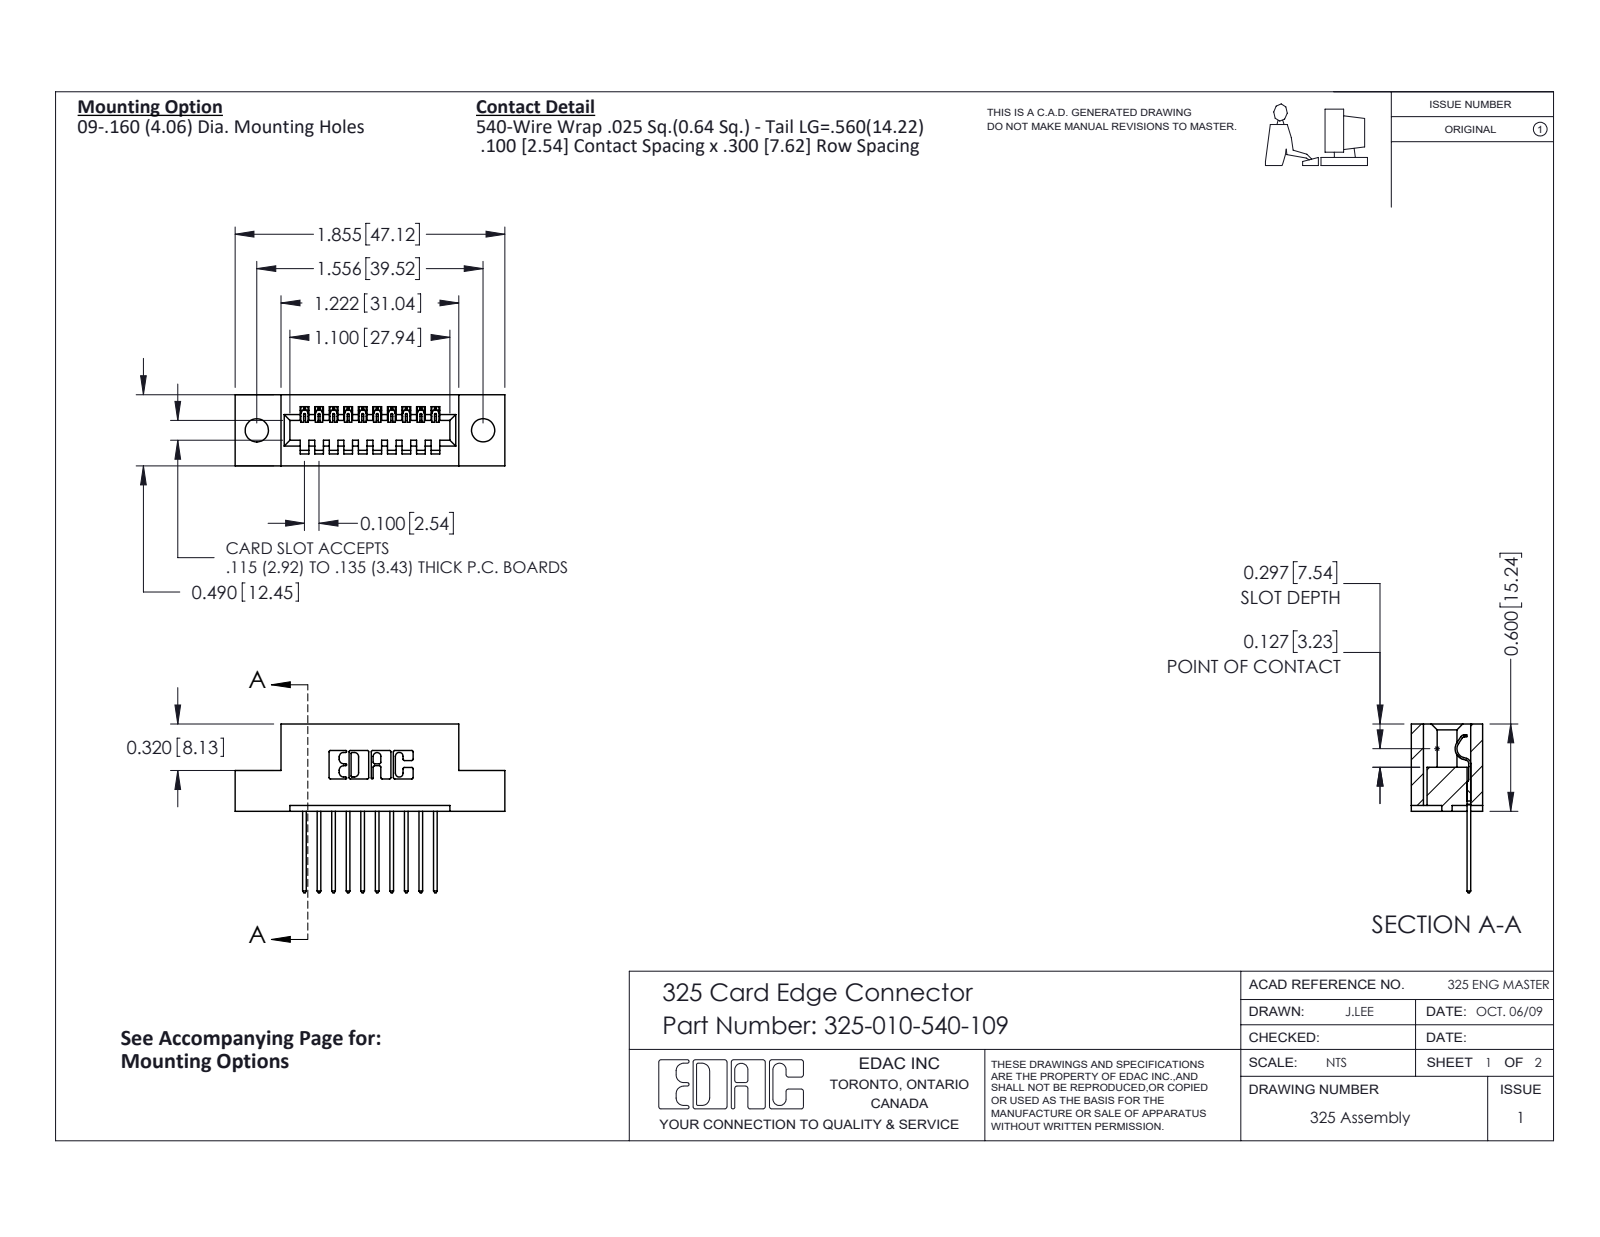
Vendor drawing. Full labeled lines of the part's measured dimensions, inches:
Part name (STEP PRODUCT): 325-010-540-109; 325-292-001_325-293-140; 325 Part_.160 TH
STEP written by: SolidWorks 2016 (CONFIG_CONTROL_DESIGN)
Units: inches
Bodies: 11 solids, 694 faces (490 planar, 204 cylindrical, 0 other)
Overall size (bounding box): 1.855 × 1.16 × 0.49
Volume: 0.336 in³ · Surface area: 8.487 in²
Round holes (diameter × count): ⌀0.16 ×2
Partial cylindrical surfaces — rounded edges, fillets, slot ends (radius × count): R0.01 ×22, R0.006 ×20, R0.01 ×20, R0.007 ×6, R0.031 ×6, R0.026 ×3, R0.014 ×1, R0.022 ×1
Main face-to-face distances: 0.3, 0.083, 0.407, 0.04, 0.1, 0.49, 0.2, 0.6, 0.4, 0.107
Hole centre spacings: 1.556
